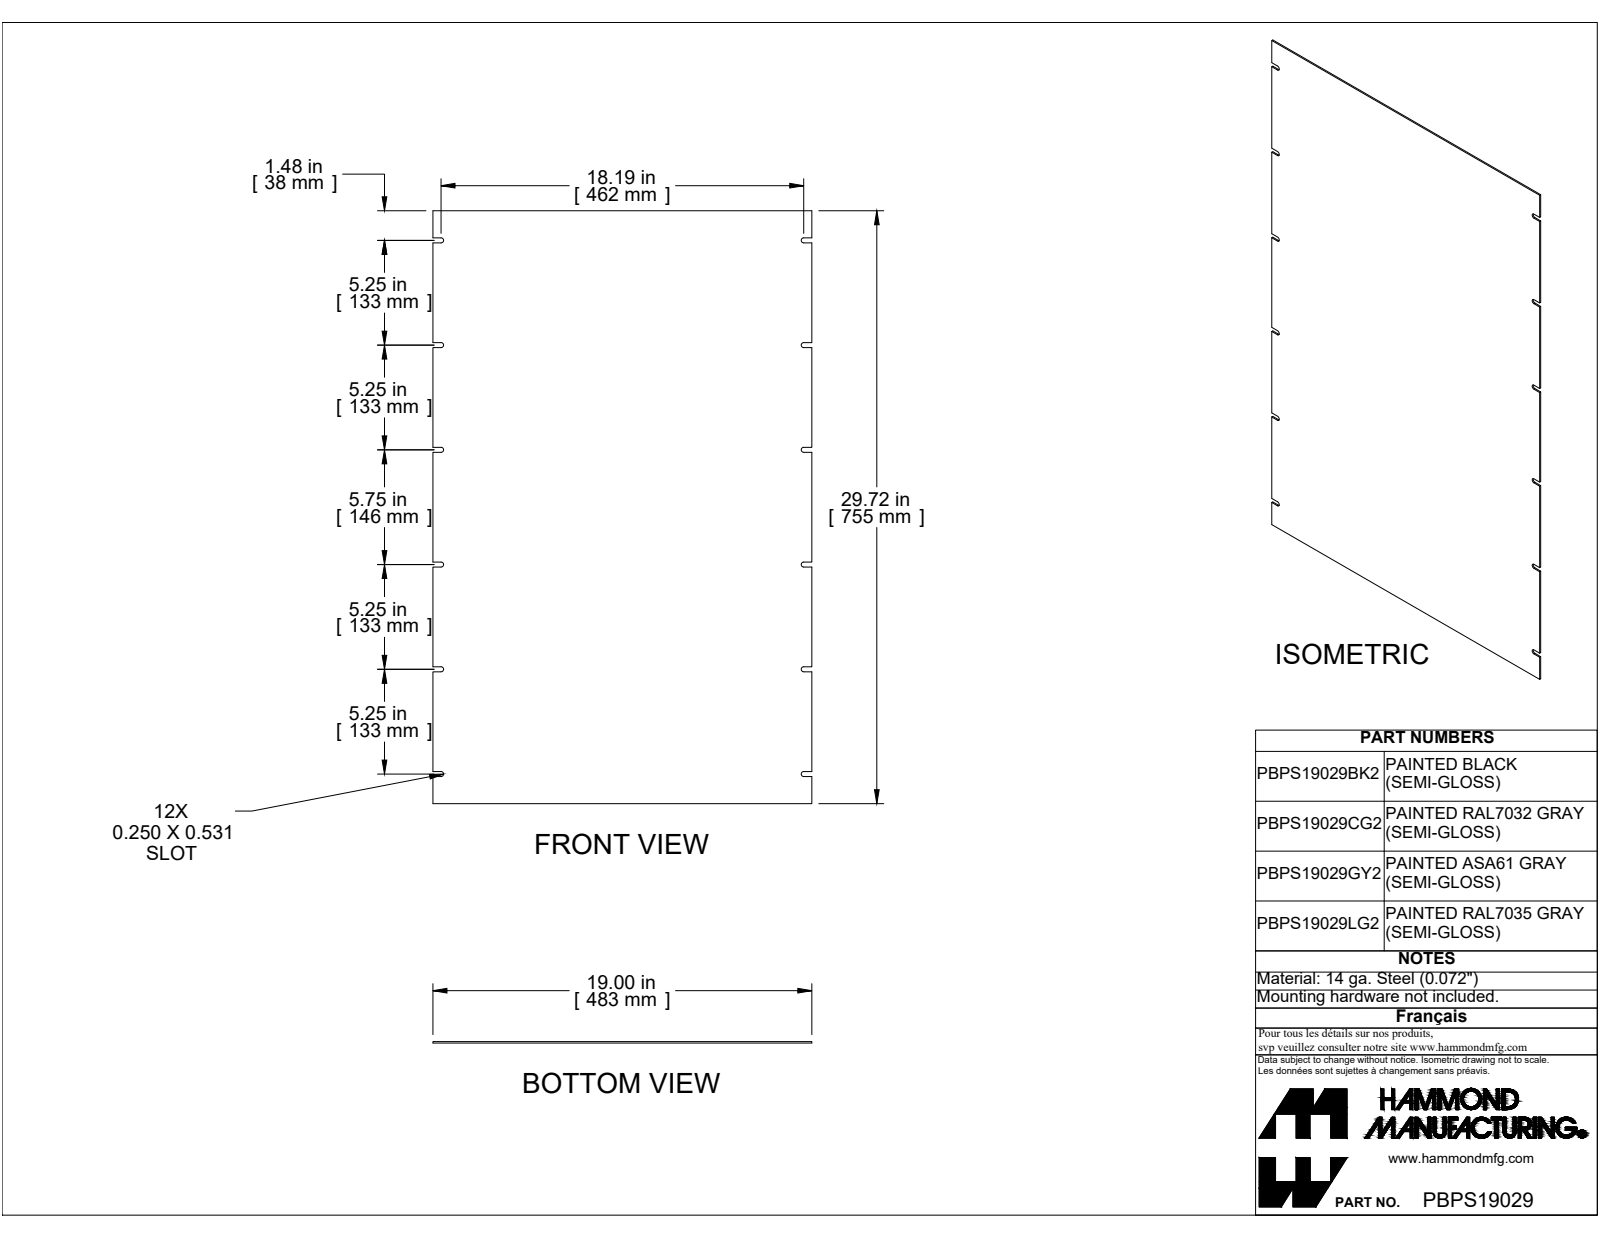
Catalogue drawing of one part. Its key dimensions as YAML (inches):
part_name: "PBPS19029LG2"
step_written_by: "SolidWorks 2019 (CONFIG_CONTROL_DESIGN)"
units: inches
bodies: {solids: 1, faces: 54, planar: 42, cylindrical: 12, other: 0}
overall_size: [29.718, 19, 0.072]
volume: 40.55
surface_area: 1134
partial_cylinders:
  - {radius: 0.125, count: 12}
face_to_face_distances: [0.072, 19, 29.718, 5.25, 0.25, 16.25, 5.5, 5, 11, 10.75]
